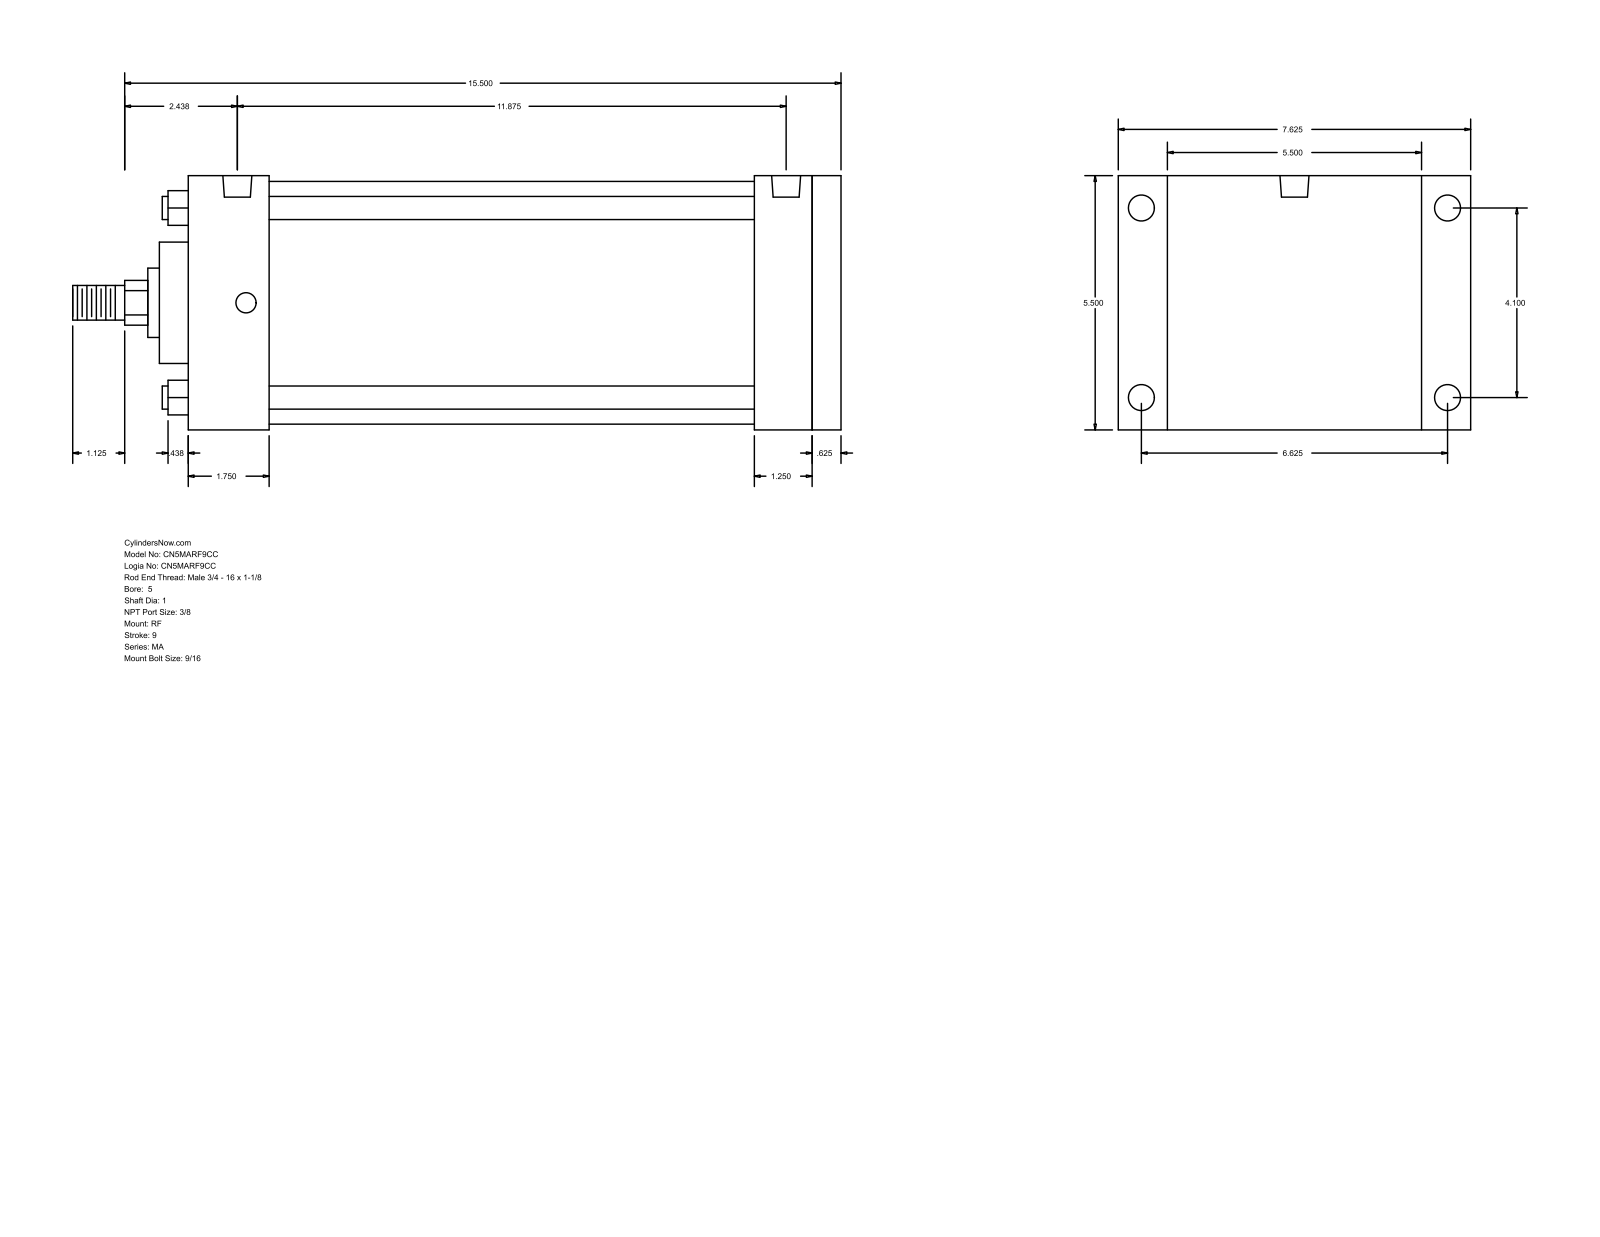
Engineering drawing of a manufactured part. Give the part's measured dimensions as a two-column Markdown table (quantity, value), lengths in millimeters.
| quantity | value |
| --- | --- |
| part name | MA_RF__0500_1 |
| STEP written by | GSSL Pune (CONFIG_CONTROL_DESIGN) |
| units | millimeters |
| bodies | 0 solids, 94 faces (65 planar, 29 cylindrical, 0 other) |
| overall size | 422.27 × 193.68 × 139.7 |
| round holes (diameter × count) | 11.11 × 4, 14.29 × 4, 15.93 × 2 |
| round bosses / shafts (diameter × count) | 12.7 × 4, 133.35 × 1, 66.67 × 1, 38.1 × 1, 25.4 × 1, 19.05 × 1 |
| partial cylindrical surfaces (radius × count) | 12.29 × 1 |
| main face-to-face distances | 139.7, 358.78, 342.9, 15.88, 44.46, 298.44, 314.32, 311.15, 266.69, 31.75 |
| hole center spacings | 104.14, 168.28, 197.9, 292.1, 4.76, 4.77, 296.86, 296.87 |
